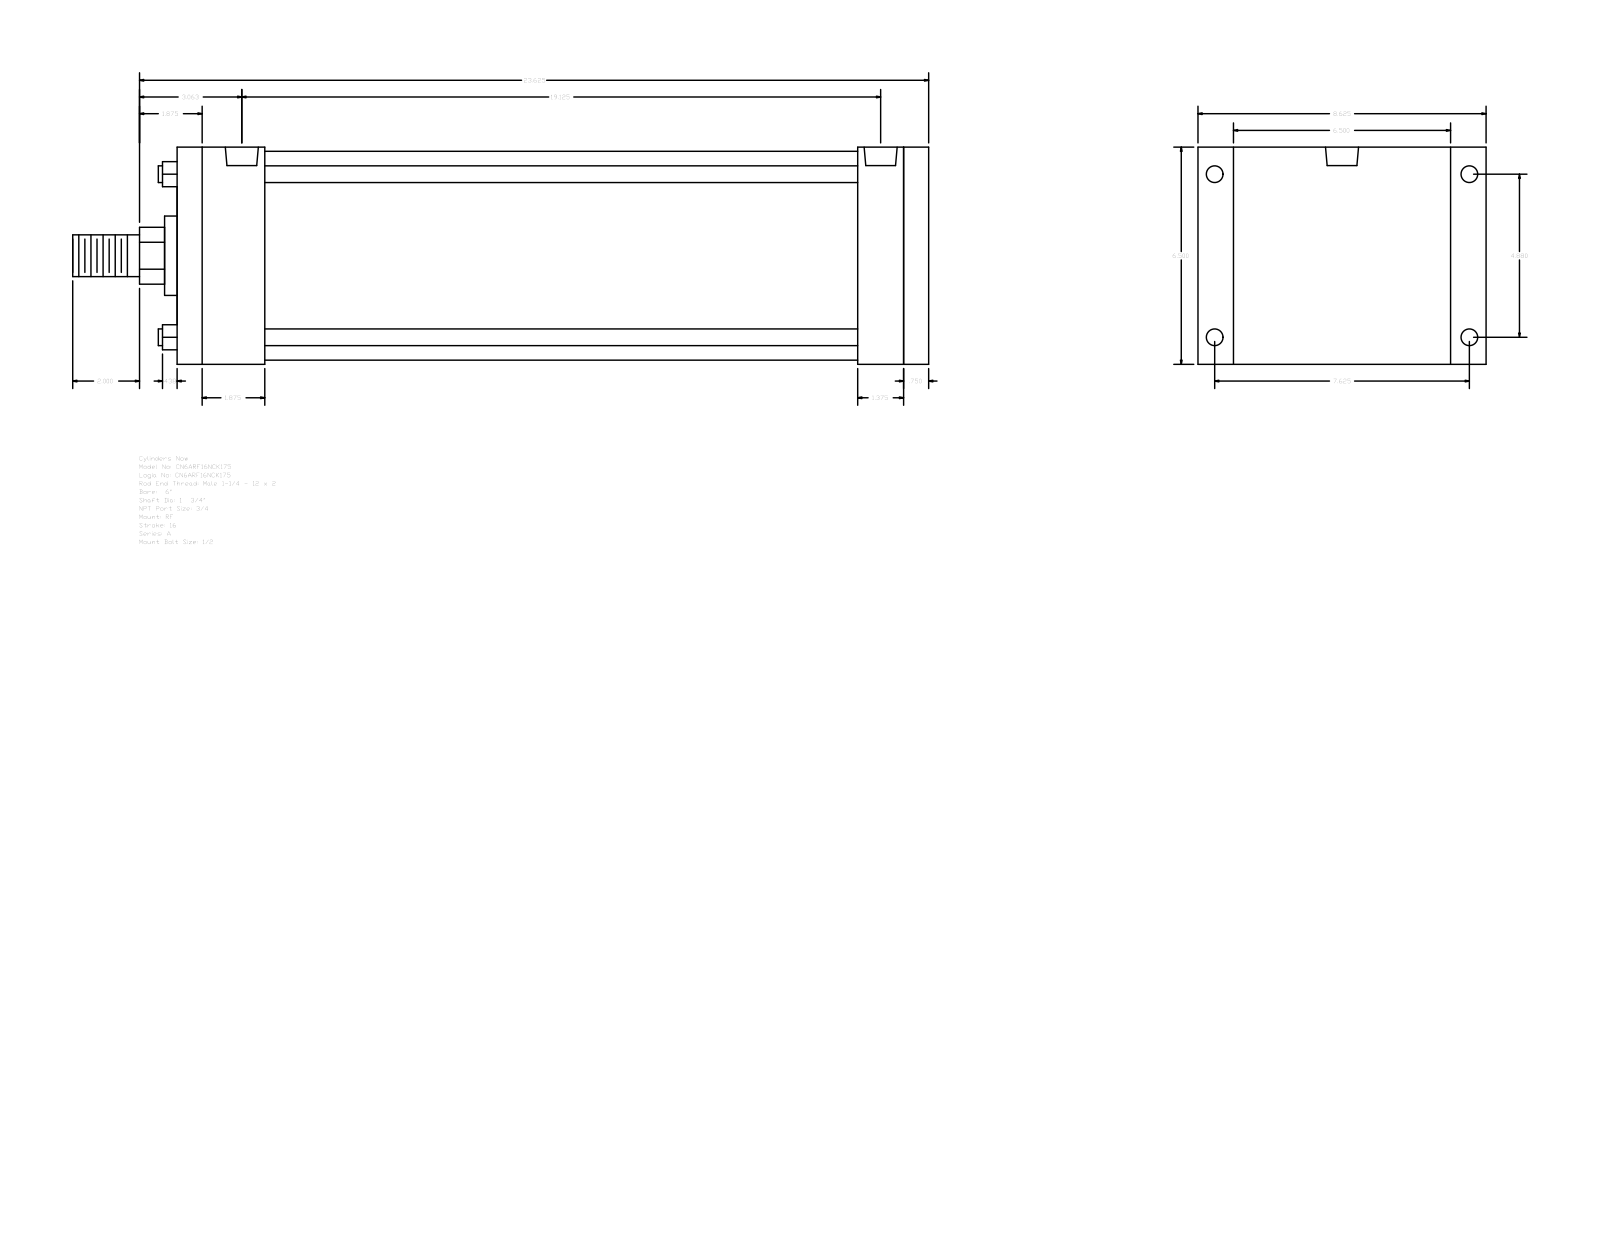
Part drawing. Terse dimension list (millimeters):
name: A_RF__0600_1.75
written by: GSSL Pune (CONFIG_CONTROL_DESIGN)
unit: mm
bodies: 0 solids, 92 faces (64 planar, 28 cylindrical, 0 other)
size: 650.88 × 219.07 × 165.1
holes: 4× ⌀12.7, 4× ⌀15.08, 2× ⌀25.12
bosses: 4× ⌀12.7, 1× ⌀158.75, 1× ⌀60.33, 1× ⌀44.45, 1× ⌀31.75
rounds: 1× R21.63
face distances: 165.1, 571.51, 552.45, 19.06, 66.68, 485.77, 504.83, 517.53, 450.85, 34.92
hole spacings: 5.56, 123.96, 193.68, 229.95, 474.65, 480.21, 485.77
